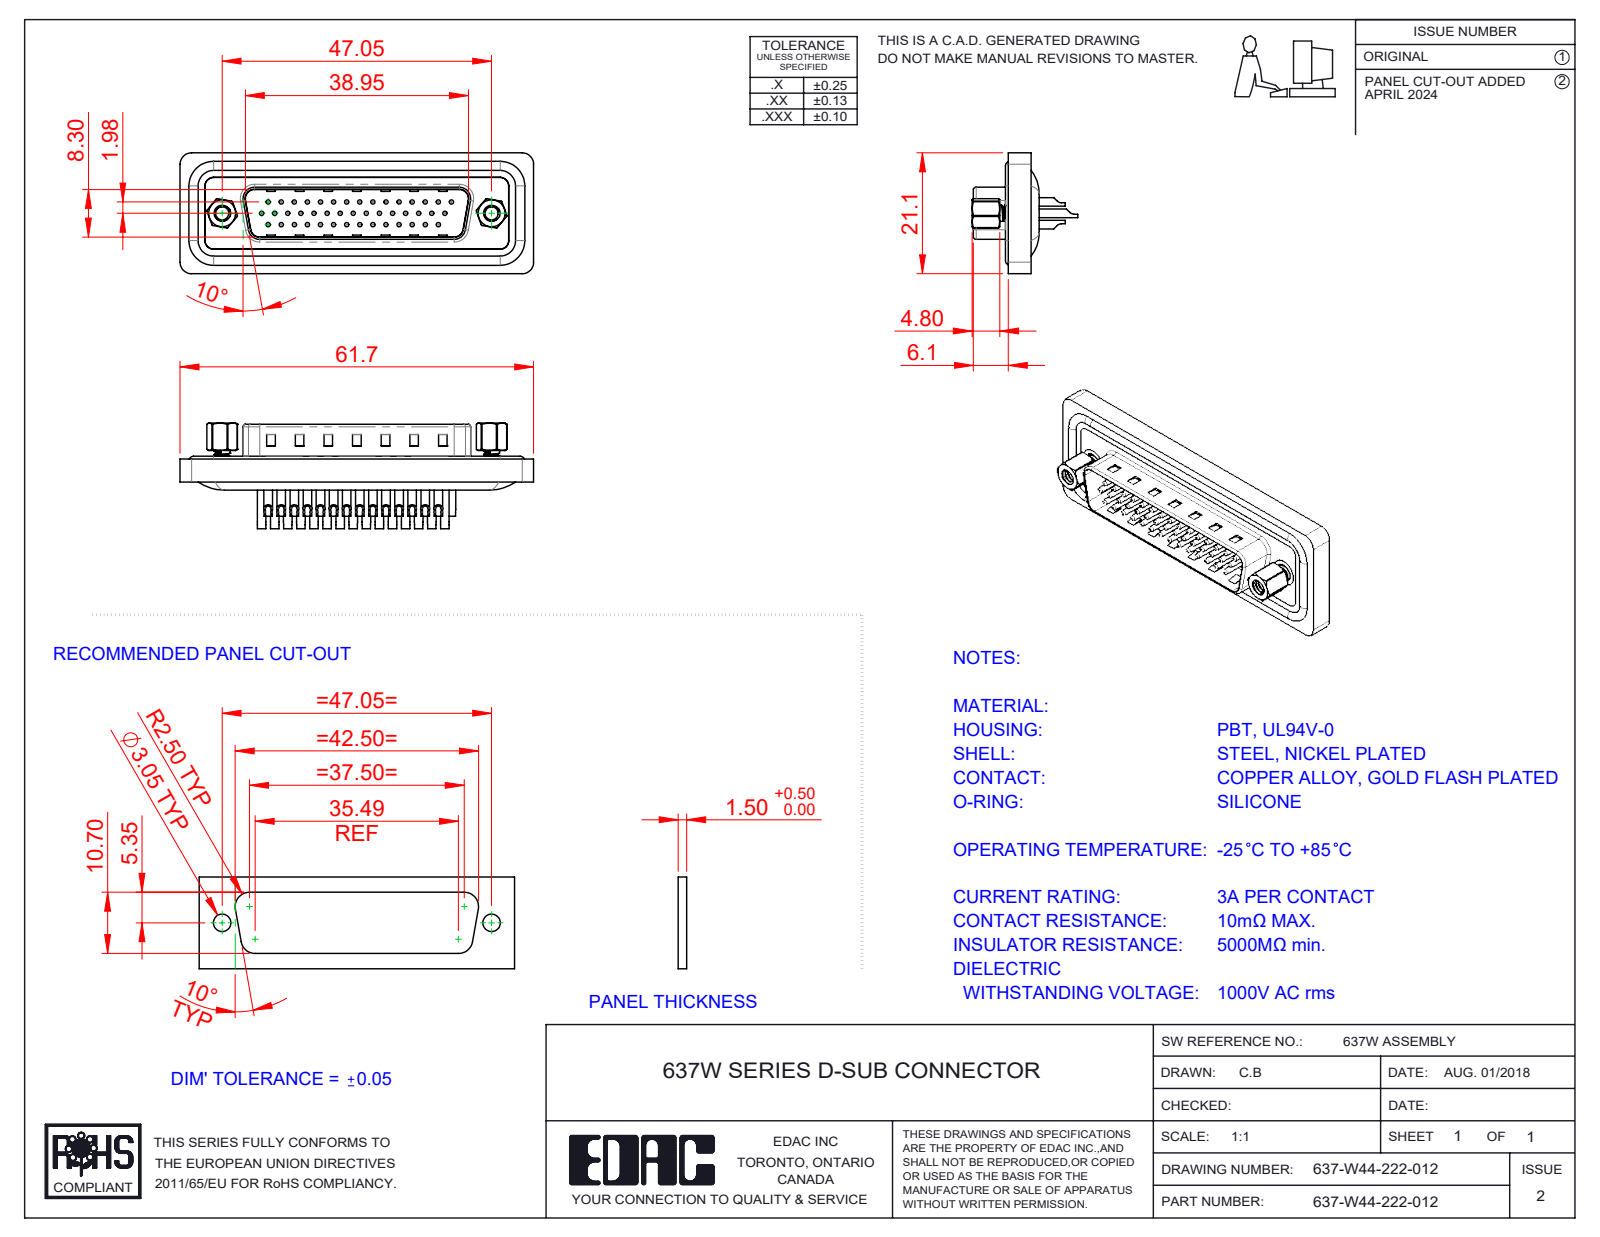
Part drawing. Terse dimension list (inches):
name: 637W Contact Row 1_22; 637W 4-40 Threaded Rivet; 637W Contact Row 3_22; 637W Waterproof Housing_44 Contacts (+5 more)
written by: SolidWorks 2023 (CONFIG_CONTROL_DESIGN)
unit: in
bodies: 52 solids, 2236 faces (601 planar, 1012 cylindrical, 623 other)
size: 2.431 × 0.831 × 0.726
volume: 0.397 in³; area: 19.45 in²
holes: 44× ⌀0.03, 44× ⌀0.039, 44× ⌀0.059, 44× ⌀0.063, 44× ⌀0.079, 2× ⌀0.089, 2× ⌀0.09, 2× ⌀0.157, 2× ⌀0.189, 2× ⌀0.197
bosses: 20× ⌀0.059, 4× ⌀0.063, 2× ⌀0.193, 2× ⌀0.11, 1× ⌀0.197
rounds: 14× R0.079, 13× R0.059, 8× R0.02, 6× R0.106, 4× R0.035, 4× R0.063, 4× R0.169, 3× R0.039
face distances: 0.016, 0.063, 0.098, 0.114, 0.043, 0.222, 0.608, 0.252, 0.579, 0.03
hole spacings: 0.09, 0.156, 0.09, 0.18, 0.324, 0.27, 0.45, 0.59
